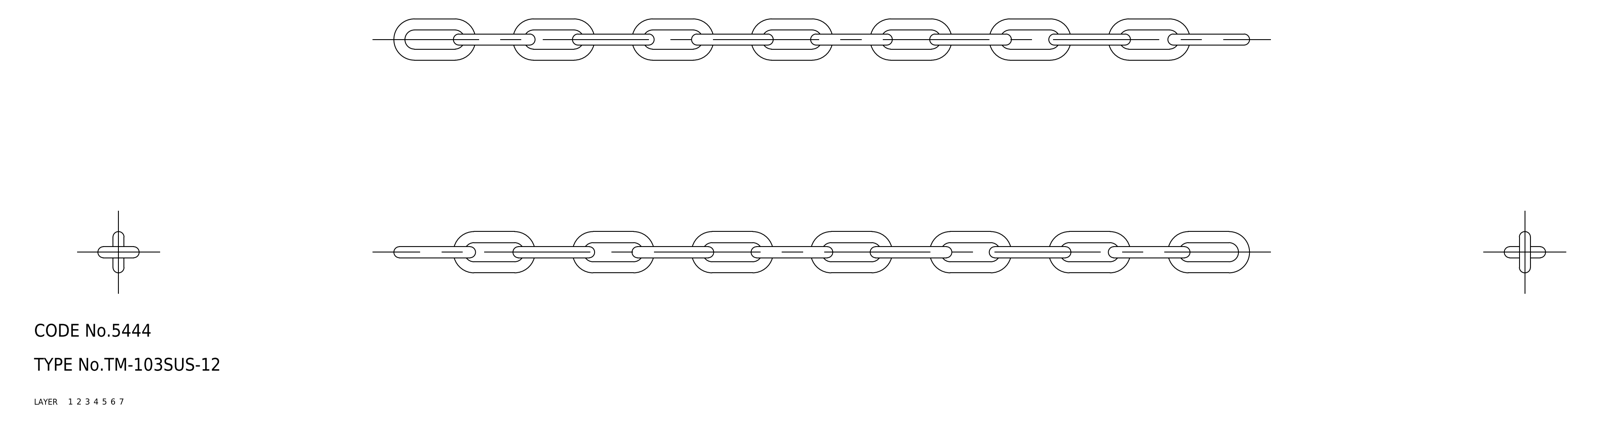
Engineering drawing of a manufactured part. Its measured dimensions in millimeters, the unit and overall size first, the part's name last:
Units: millimetres
Overall size (bounding box): 201.2 × 9.7 × 9.7
Volume: 3 083 mm³ · Surface area: 4 726 mm²
Bodies: 14 solids, 112 faces (0 planar, 0 cylindrical, 112 other)
Part name (STEP PRODUCT): chain; TM_103SUS_12_11417_36
STEP written by: CADfix (AUTOMOTIVE_DESIGN)
